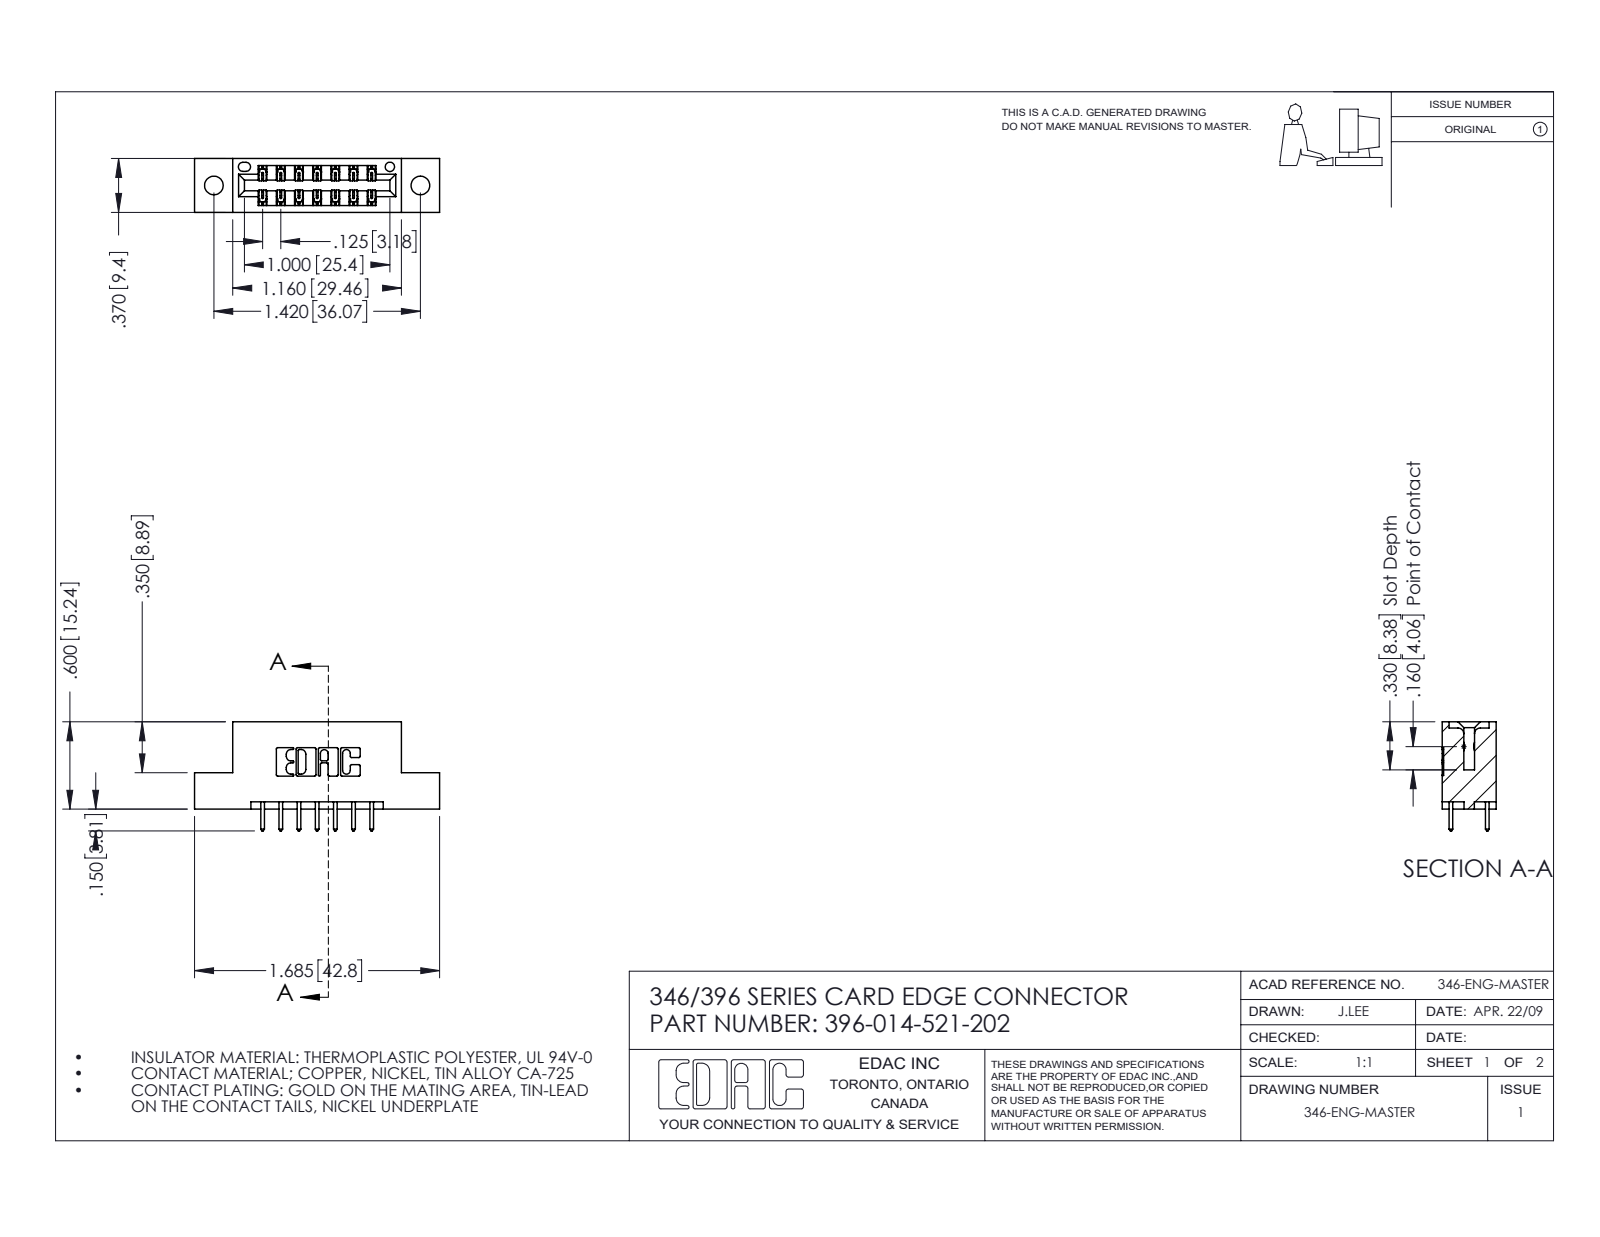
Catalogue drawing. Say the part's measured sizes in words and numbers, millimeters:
The part is named "396-014-521-202; 345-292-001_345-293-121; 346 Part_Flush Mounting Lugs - 0.128 Dia". Its 3-D file was written by "SolidWorks 2016 (CONFIG_CONTROL_DESIGN)". It is 15 solids with 850 faces: 566 planar, 284 cylindrical and 0 other. Overall it measures 42.8 by 19.1 by 9.4 millimeters. Its volume is 3 870 cubic millimeters and its surface area 4 447 square millimeters. Round holes: 2 of diameter 3.3, 1 of diameter 1.6. Partial cylindrical surfaces (rounded edges, fillets, slot ends): 22 of radius 0.3, 21 of radius 0.2, 14 of radius 0.3, 6 of radius 0.2, 6 of radius 0.8, 3 of radius 0.7, 2 of radius 0.4, 2 of radius 0.6. The main face-to-face distances are 6.4, 1.2, 8.2, 9.4, 1.8, 7.6, 0.6, 7, 3.8, 5.6. The hole center spacings are 6.2, 30.9, 36.1.
